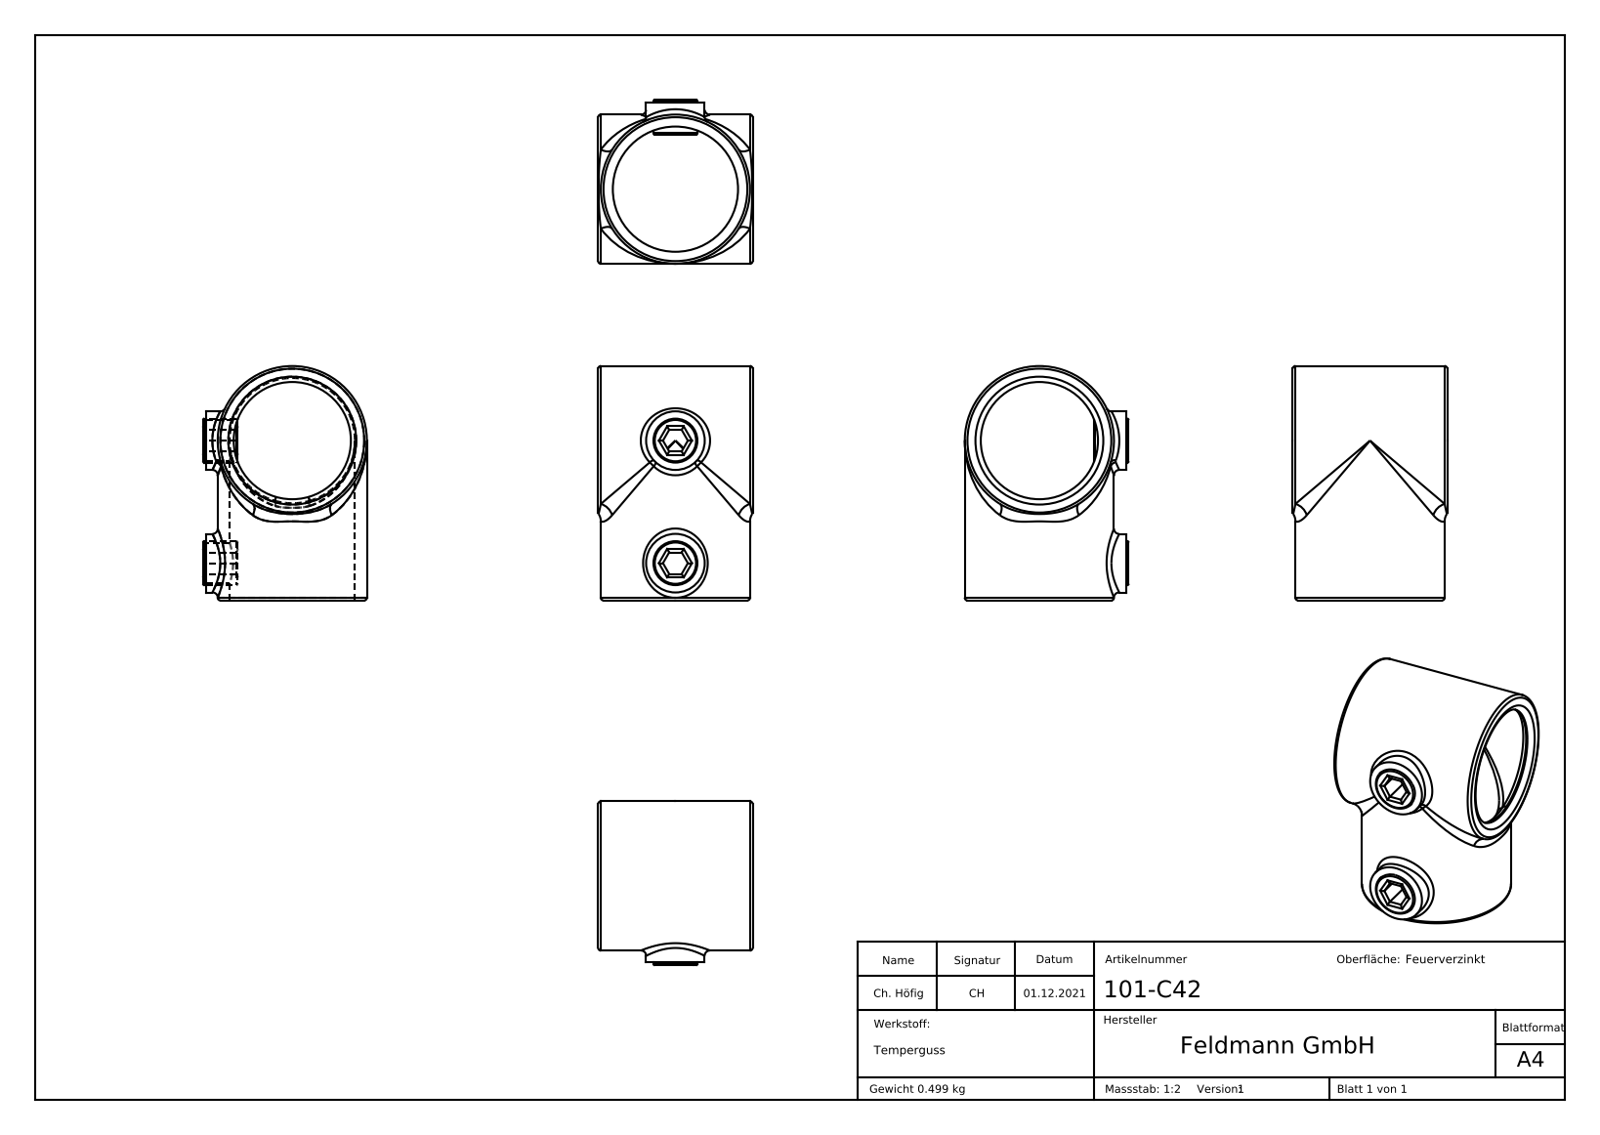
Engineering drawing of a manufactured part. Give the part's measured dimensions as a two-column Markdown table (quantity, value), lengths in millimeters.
| quantity | value |
| --- | --- |
| part name | 101-C42 Teil1; 101-C42; 101-C42 Teil2 |
| STEP written by | SolidWorks 2018 (CONFIG_CONTROL_DESIGN) |
| units | millimeters |
| bodies | 3 solids, 87 faces (21 planar, 36 cylindrical, 30 other) |
| overall size | 88 × 61.5 × 58 |
| volume | 68 018 mm³ |
| surface area | 33 095 mm² |
| round holes (diameter × count) | 15.25 × 2, 47 × 2, 44 × 1 |
| round bosses / shafts (diameter × count) | 56 × 2, 22 × 2, 16.5 × 2 |
| partial cylindrical surfaces (radius × count) | 2 × 24 |
| main face-to-face distances | 58, 8.1, 23, 12, 13, 1, 46, 31.1, 14.9, 18.05 |
| hole center spacings | 46 |
